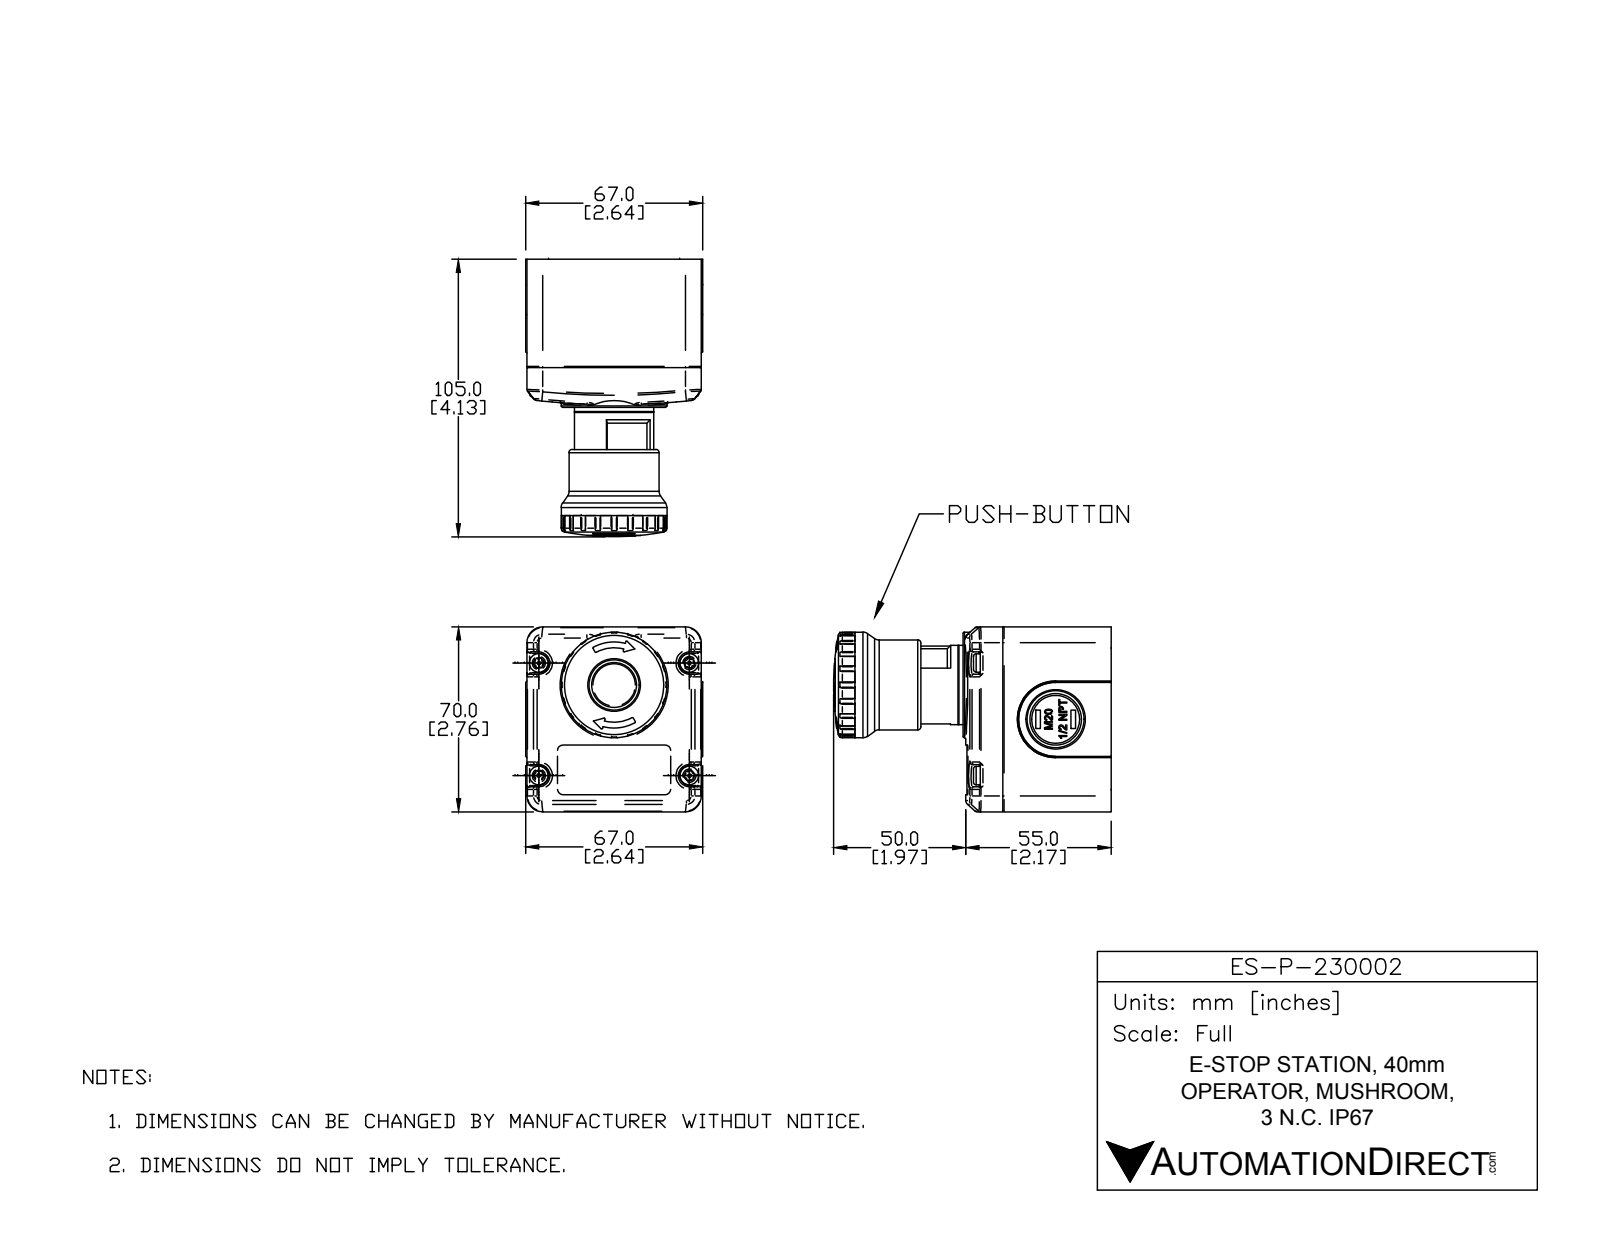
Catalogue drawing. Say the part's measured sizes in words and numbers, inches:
The part is named "ES-P-230002". Its 3-D file was written by "SolidWorks 2016 (AUTOMOTIVE_DESIGN)". It is 11 solids with 990 faces: 353 planar, 286 cylindrical and 351 other. Overall it measures 4.134 by 2.756 by 2.638 inches. Its volume is 17.36 cubic inches and its surface area 75.57 square inches. Round holes: 4 of diameter 0.173, 1 of diameter 0.846, 1 of diameter 1.224. Round bosses or shafts: 4 of diameter 0.276, 4 of diameter 0.039, 1 of diameter 1.575, 1 of diameter 1.339, 1 of diameter 1.181, 1 of diameter 0.787. Partial cylindrical surfaces (rounded edges, fillets, slot ends): 80 of radius 0.004, 24 of radius 0.03, 14 of radius 0.02, 8 of radius 0.039, 6 of radius 0.079, 4 of radius 0.008, 4 of radius 0.165, 4 of radius 0.236. The main face-to-face distances are 1.583, 2.756, 2.598, 2.173, 0.591, 0.02, 0.079, 2.52, 2.236, 0.654. The hole center spacings are 1.235, 1.966, 2.126, 2.283, 3.12.
